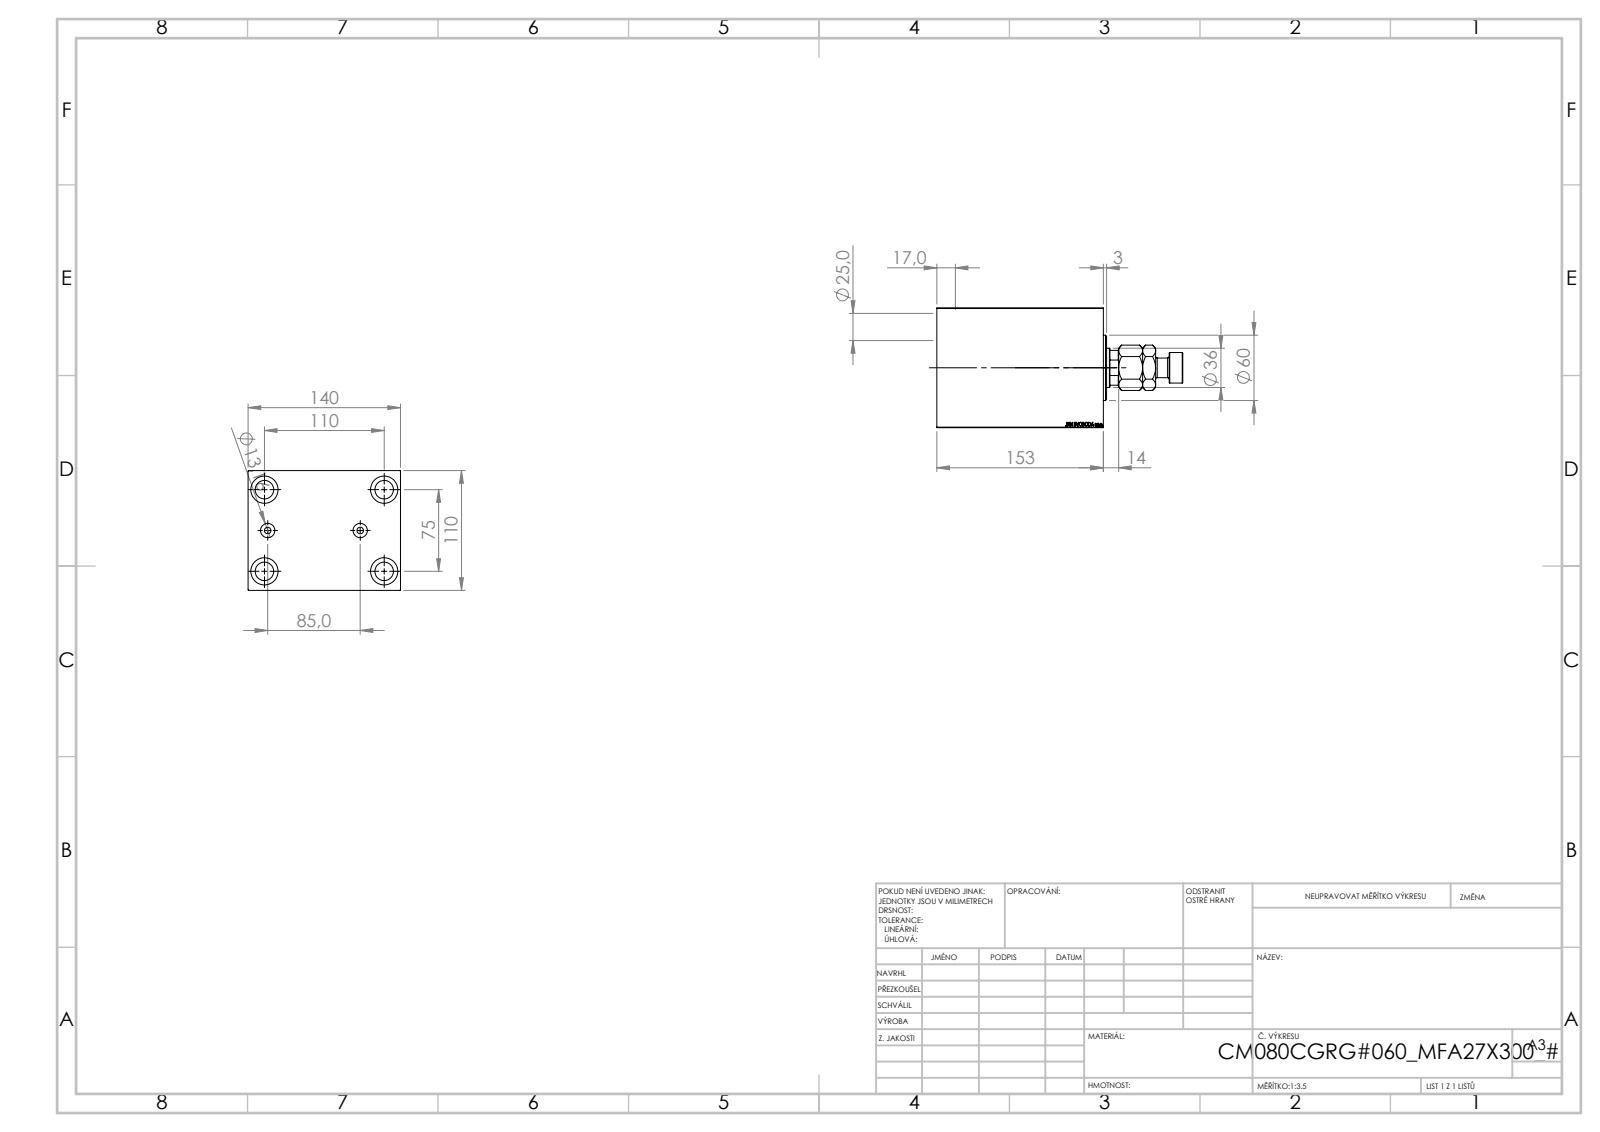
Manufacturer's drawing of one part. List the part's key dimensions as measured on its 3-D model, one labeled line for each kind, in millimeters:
Part name (STEP PRODUCT): V450CM_C_VCP; V450CM_VC_B; MFA; V450CM_C_Body
STEP written by: SolidWorks 2019 (CONFIG_CONTROL_DESIGN)
Units: millimetres
Bodies: 4 solids, 915 faces (427 planar, 62 cylindrical, 426 other)
Overall size (bounding box): 225 × 140 × 110
Volume: 2 179 000 mm³ · Surface area: 209 692 mm²
Round holes (diameter × count): ⌀17 ×4, ⌀25 ×4, ⌀6 ×2, ⌀13.16 ×2, ⌀25.5 ×1, ⌀36 ×1, ⌀39.5 ×1, ⌀80 ×1, ⌀82 ×1, ⌀87 ×1
Round bosses / shafts (diameter × count): ⌀60 ×1, ⌀28 ×1, ⌀18 ×1
Partial cylindrical surfaces — rounded edges, fillets, slot ends (radius × count): R17.5 ×1
Main face-to-face distances: 110, 140, 153, 51, 102, 10, 21.6, 29.4, 131.4, 121.4
Hole centre spacings: 39.53, 66.57, 104.46, 42.5, 75, 110, 133.14, 85
